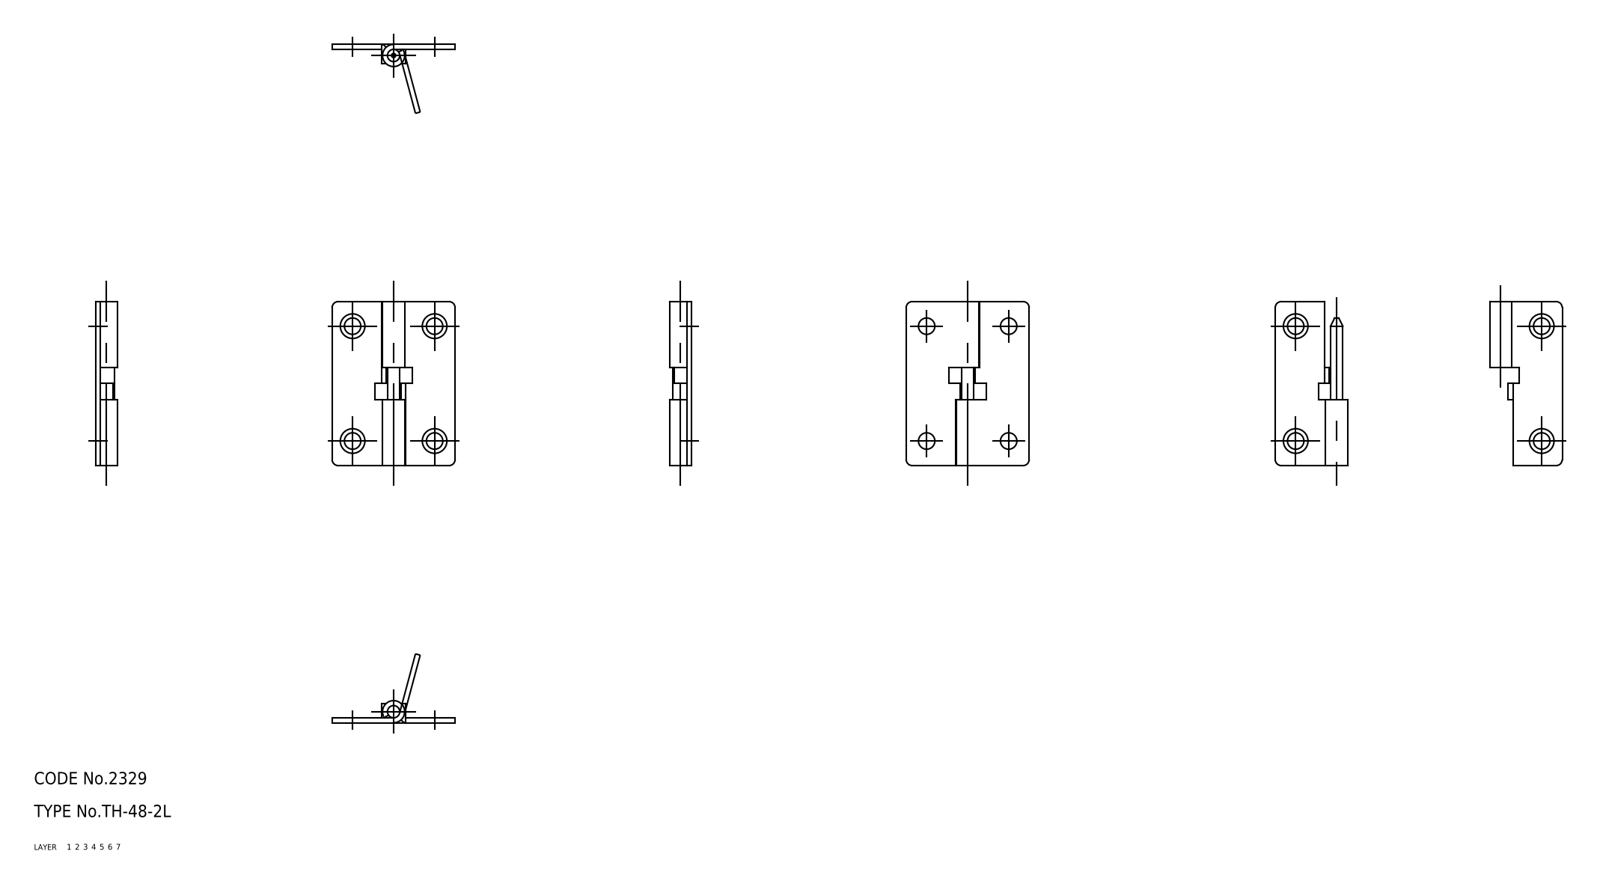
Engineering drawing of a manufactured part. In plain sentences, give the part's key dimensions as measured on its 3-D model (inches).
The part is named "shaft; hinge piece_B; hinge piece_A; TH_48_2L_10202_36". Its 3-D file was written by "CADfix (AUTOMOTIVE_DESIGN)". It is 3 solids with 60 faces: 0 planar, 0 cylindrical and 60 other. Overall it measures 1.575 by 1.181 by 0.213 inches. Its volume is 0.114 cubic inches and its surface area 5.399 square inches.
